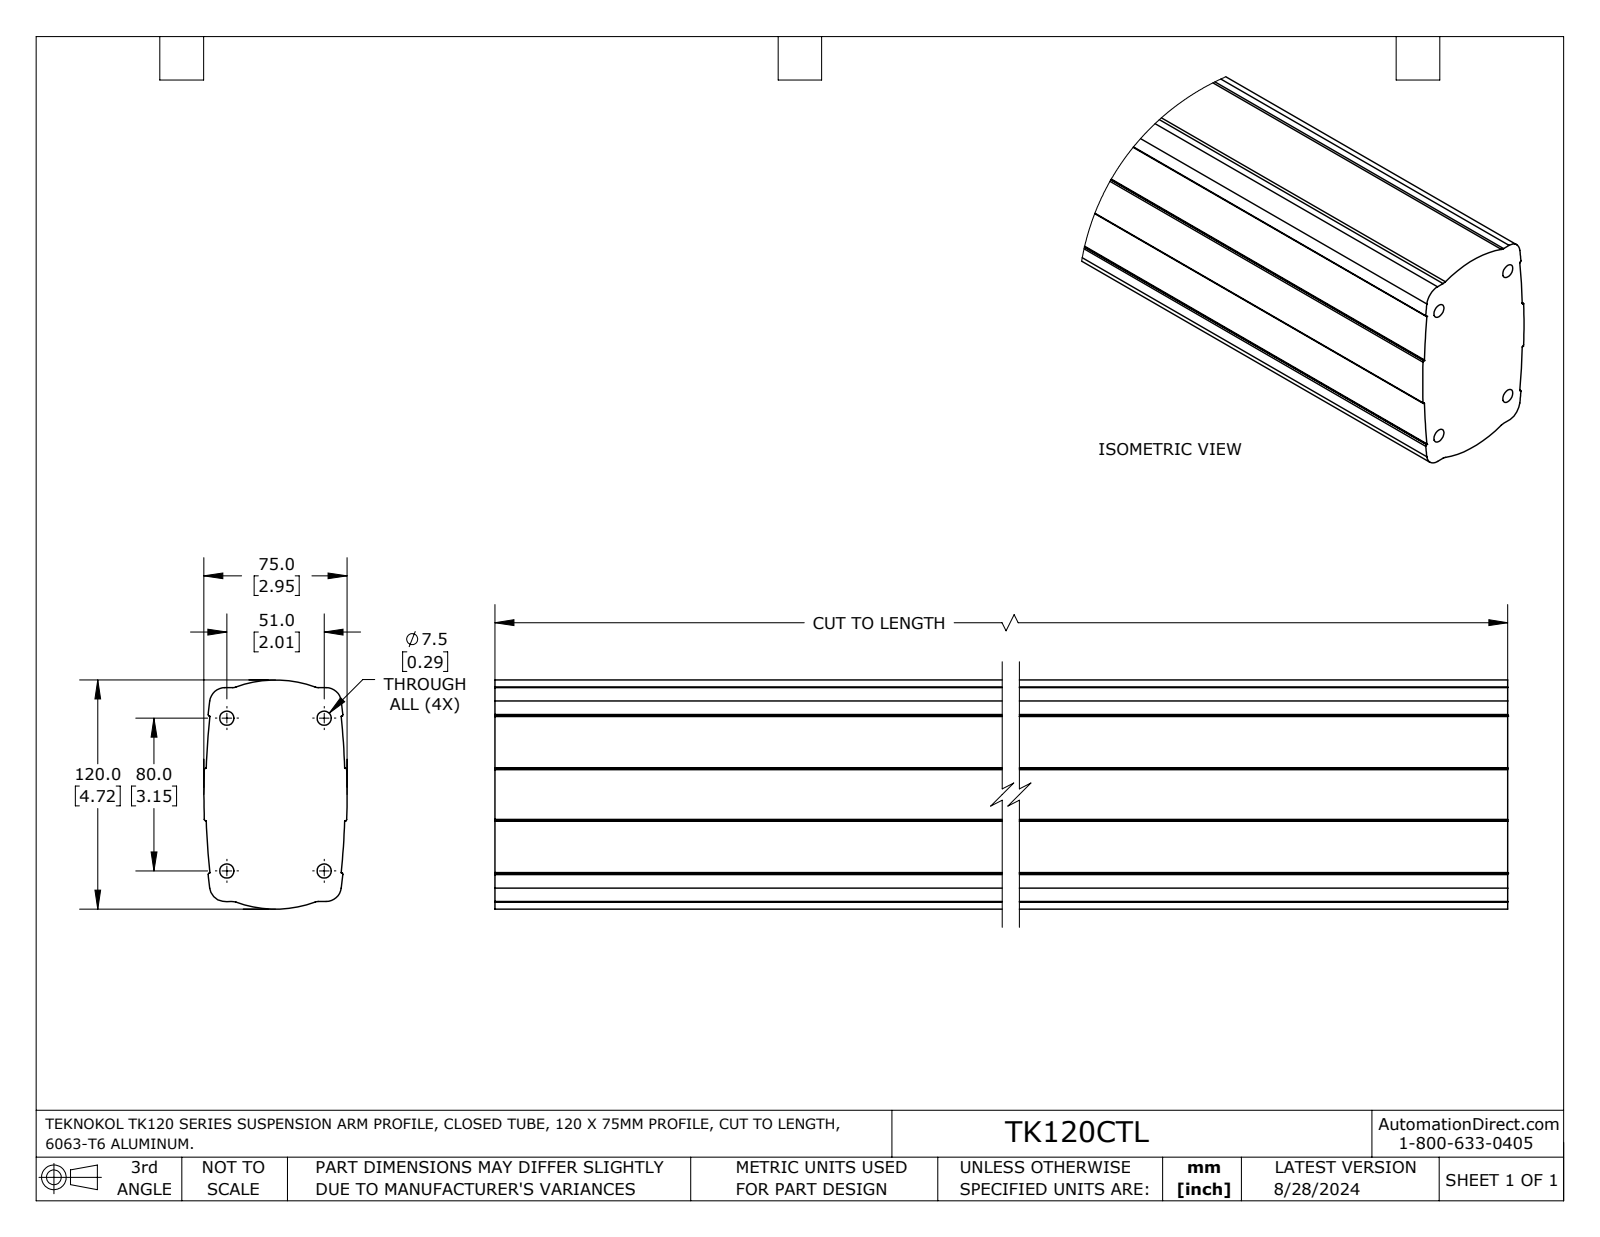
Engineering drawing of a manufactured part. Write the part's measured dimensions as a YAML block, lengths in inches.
part_name: "TK120.200"
step_written_by: "SolidWorks 2023 (AUTOMOTIVE_DESIGN)"
units: inches
bodies: {solids: 1, faces: 52, planar: 13, cylindrical: 38, other: 1}
overall_size: [78.74, 4.724, 2.953]
volume: 977.4
surface_area: 1416
round_holes:
  - {diameter: 0.293, count: 4}
partial_cylinders:
  - {radius: 0.01, count: 8}
  - {radius: 0.028, count: 8}
  - {radius: 0.197, count: 3}
  - {radius: 0.315, count: 3}
  - {radius: 15.472, count: 2}
  - {radius: 15.512, count: 2}
  - {radius: 2.362, count: 1}
face_to_face_distances: [4.409, 78.74, 2.935, 0.979]
hole_center_spacings: [2.008, 3.15, 3.735]
